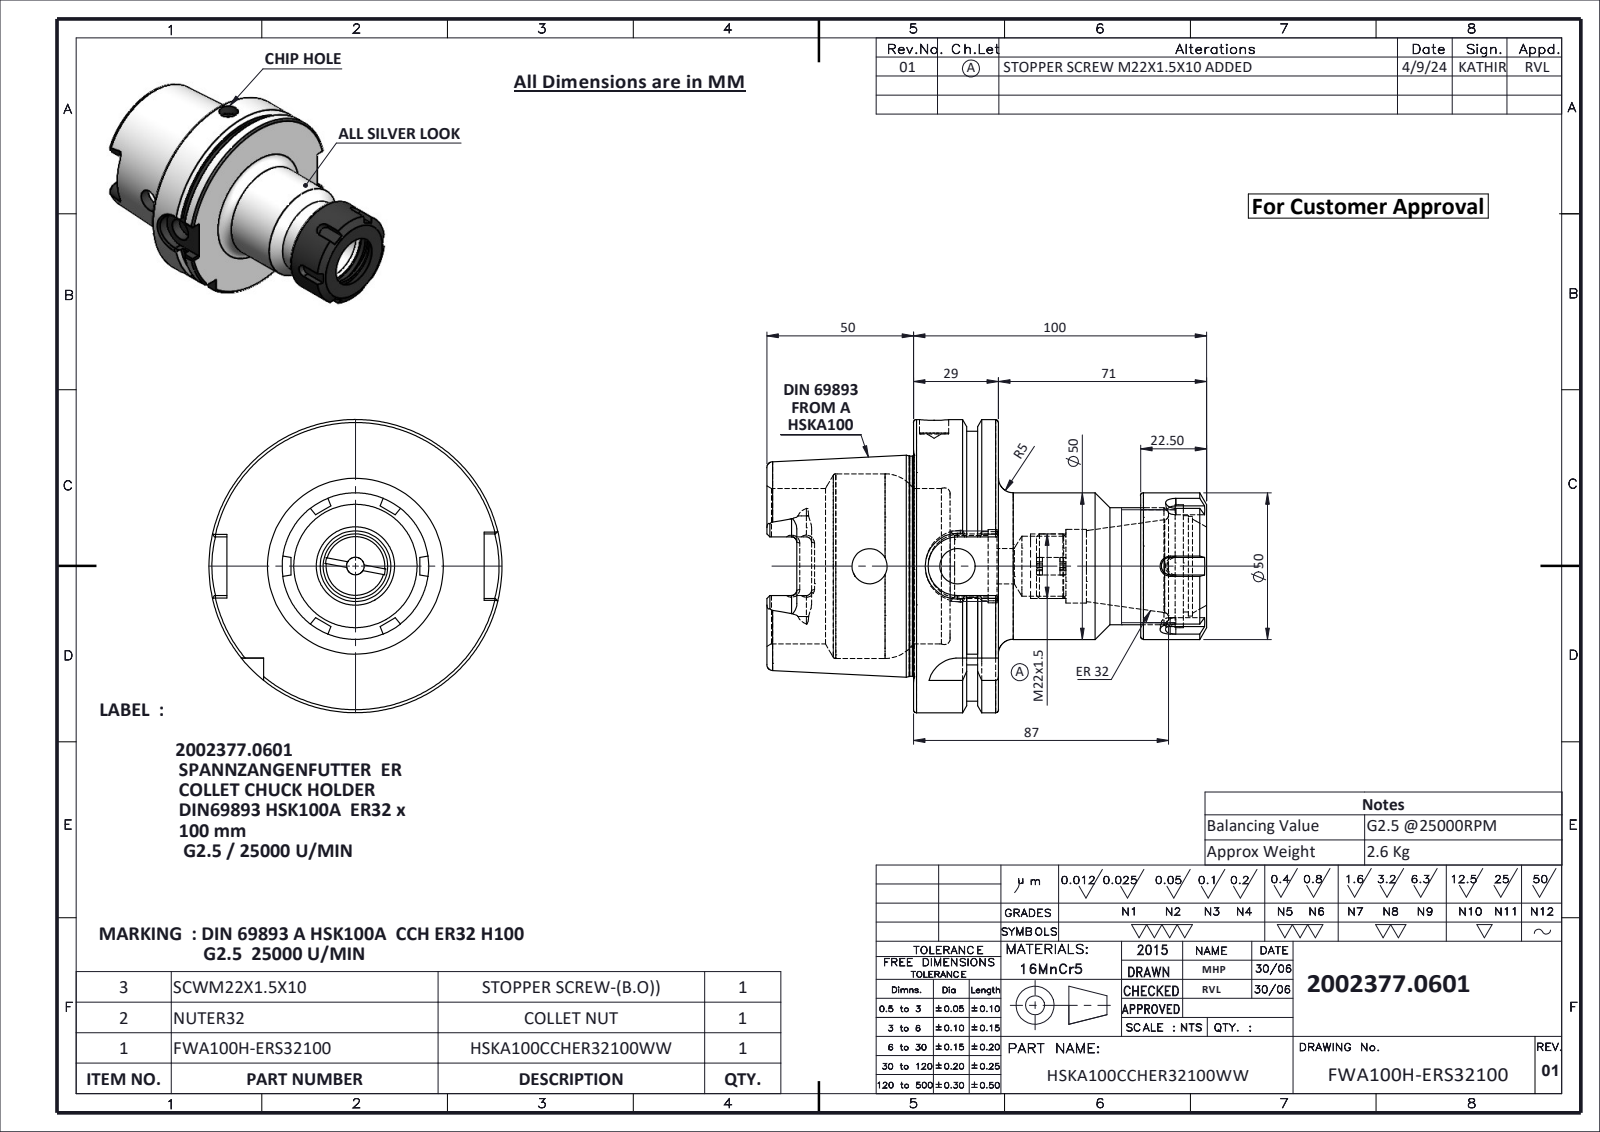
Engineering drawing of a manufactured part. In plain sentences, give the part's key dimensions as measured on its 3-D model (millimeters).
The part is named "FTNUTER32; FWA100H-ERS32100; HSKA100CCHER32100WW; SCWM22X1.5-10". Its 3-D file was written by "SolidWorks 2024 (CONFIG_CONTROL_DESIGN)". It is 3 solids with 259 faces: 95 planar, 68 cylindrical and 96 other. Overall it measures 150 by 100 by 100 millimeters. Its volume is 347 327 cubic millimeters and its surface area 72 136 square millimeters. Round holes: 3 of diameter 12, 1 of diameter 6, 1 of diameter 10, 1 of diameter 20.5, 1 of diameter 21, 1 of diameter 25, 1 of diameter 25.2, 1 of diameter 32.8, 1 of diameter 34, 1 of diameter 38.5, 1 of diameter 42, 1 of diameter 53. Round bosses or shafts: 1 of diameter 100, 1 of diameter 92, 1 of diameter 75.16, 1 of diameter 50, 1 of diameter 40, 1 of diameter 22. Partial cylindrical surfaces (rounded edges, fillets, slot ends): 6 of radius 1.8, 4 of radius 4.88, 2 of radius 10, 1 of radius 11. The main face-to-face distances are 29, 16.5, 12.5, 50, 62.5, 79, 150, 100, 87.5, 71. The hole center spacings are 1.6, 30.
